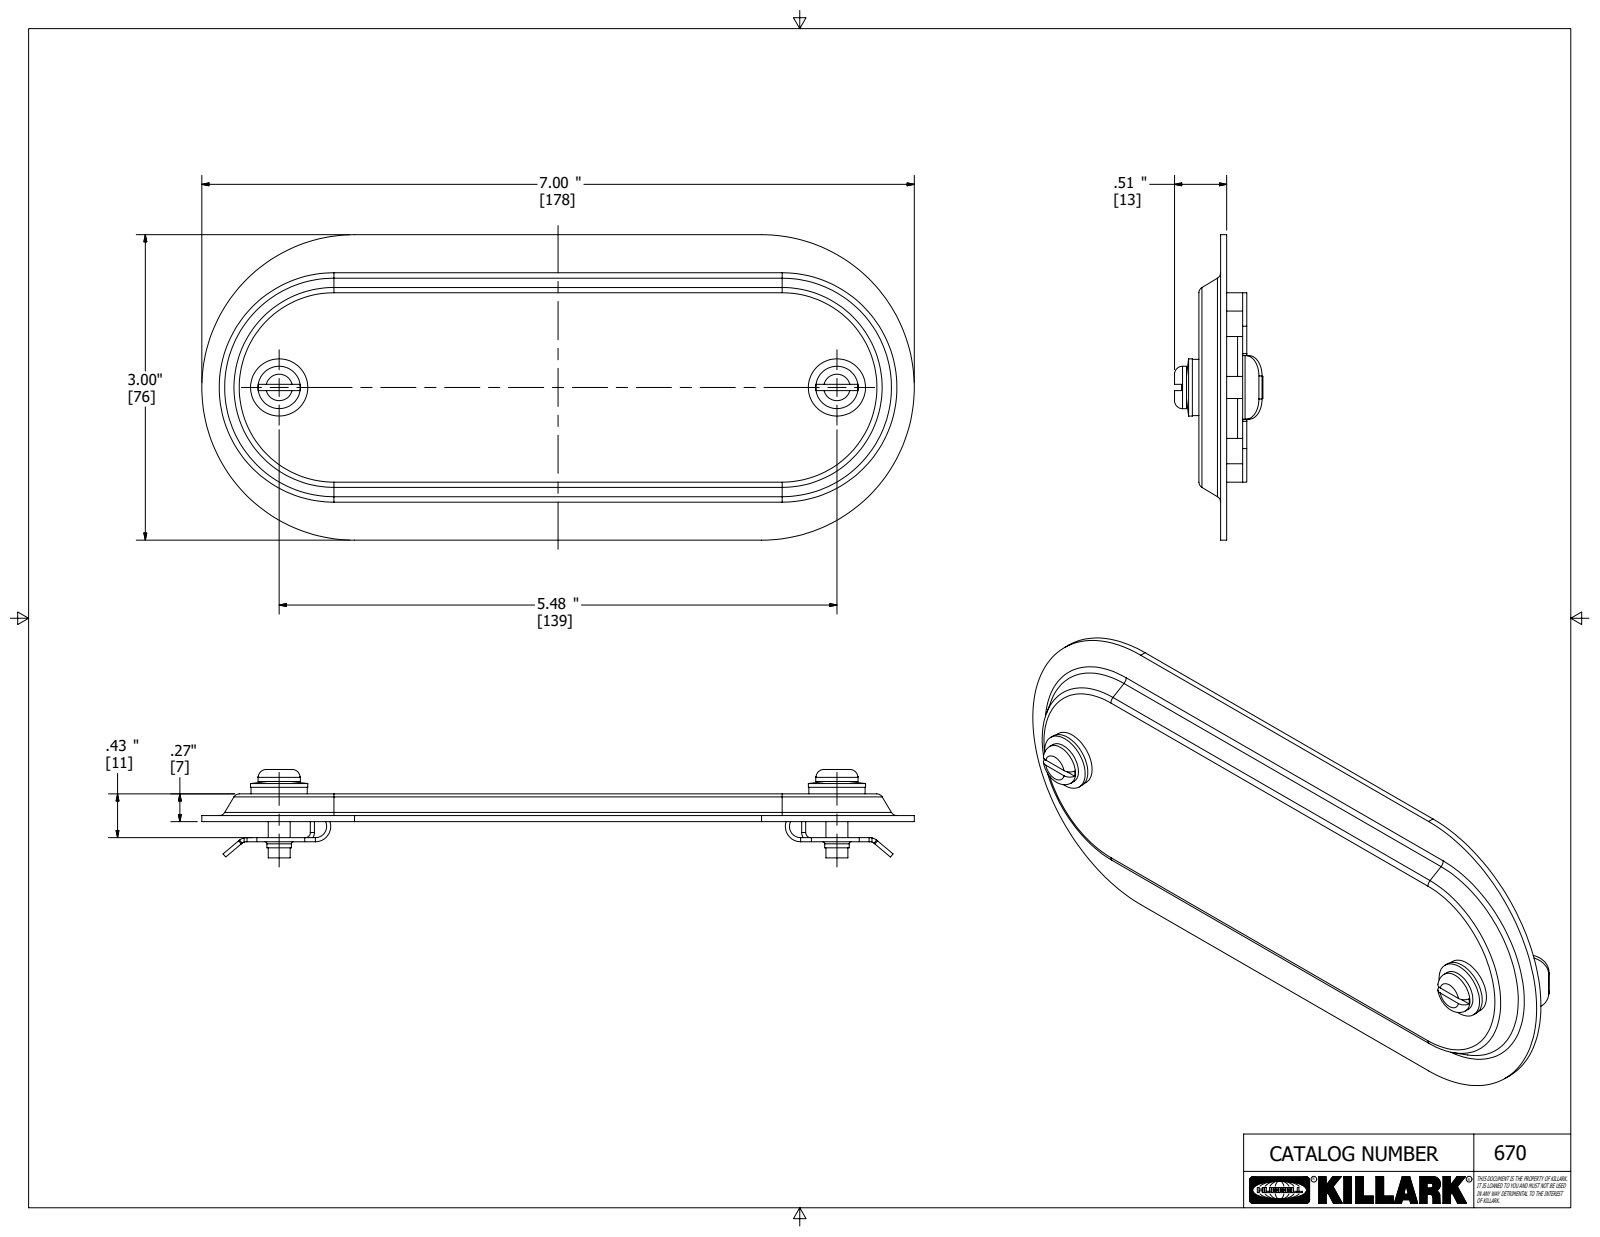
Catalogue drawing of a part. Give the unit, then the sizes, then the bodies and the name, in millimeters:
Units: millimetres
Overall size (bounding box): 177.8 × 76.2 × 22.1
Round holes (diameter × count): ⌀4.2 ×2, ⌀5.1 ×2, ⌀5.8 ×2, ⌀6.1 ×2
Round bosses / shafts (diameter × count): ⌀14.3 ×2, ⌀14 ×2, ⌀10.6 ×2, ⌀6.1 ×2, ⌀5.5 ×2
Partial cylindrical surfaces — rounded edges, fillets, slot ends (radius × count): R1.5 ×12, R12.7 ×6, R0.8 ×4, R1.6 ×4, R5.1 ×4, R1.3 ×2, R2.3 ×2, R2.6 ×2
Main face-to-face distances: 1.6, 1.5, 3.8, 5.4, 5.3, 6.9, 1, 4, 5.5, 9.3
Hole centre spacings: 139.2
Volume: 24 910 mm³ · Surface area: 34 950 mm²
Bodies: 9 solids, 208 faces (90 planar, 70 cylindrical, 48 other)
Part name (STEP PRODUCT): 670; 18395; 18038FAAB; 18023
STEP written by: Autodesk Inventor 2018 (AUTOMOTIVE_DESIGN)
